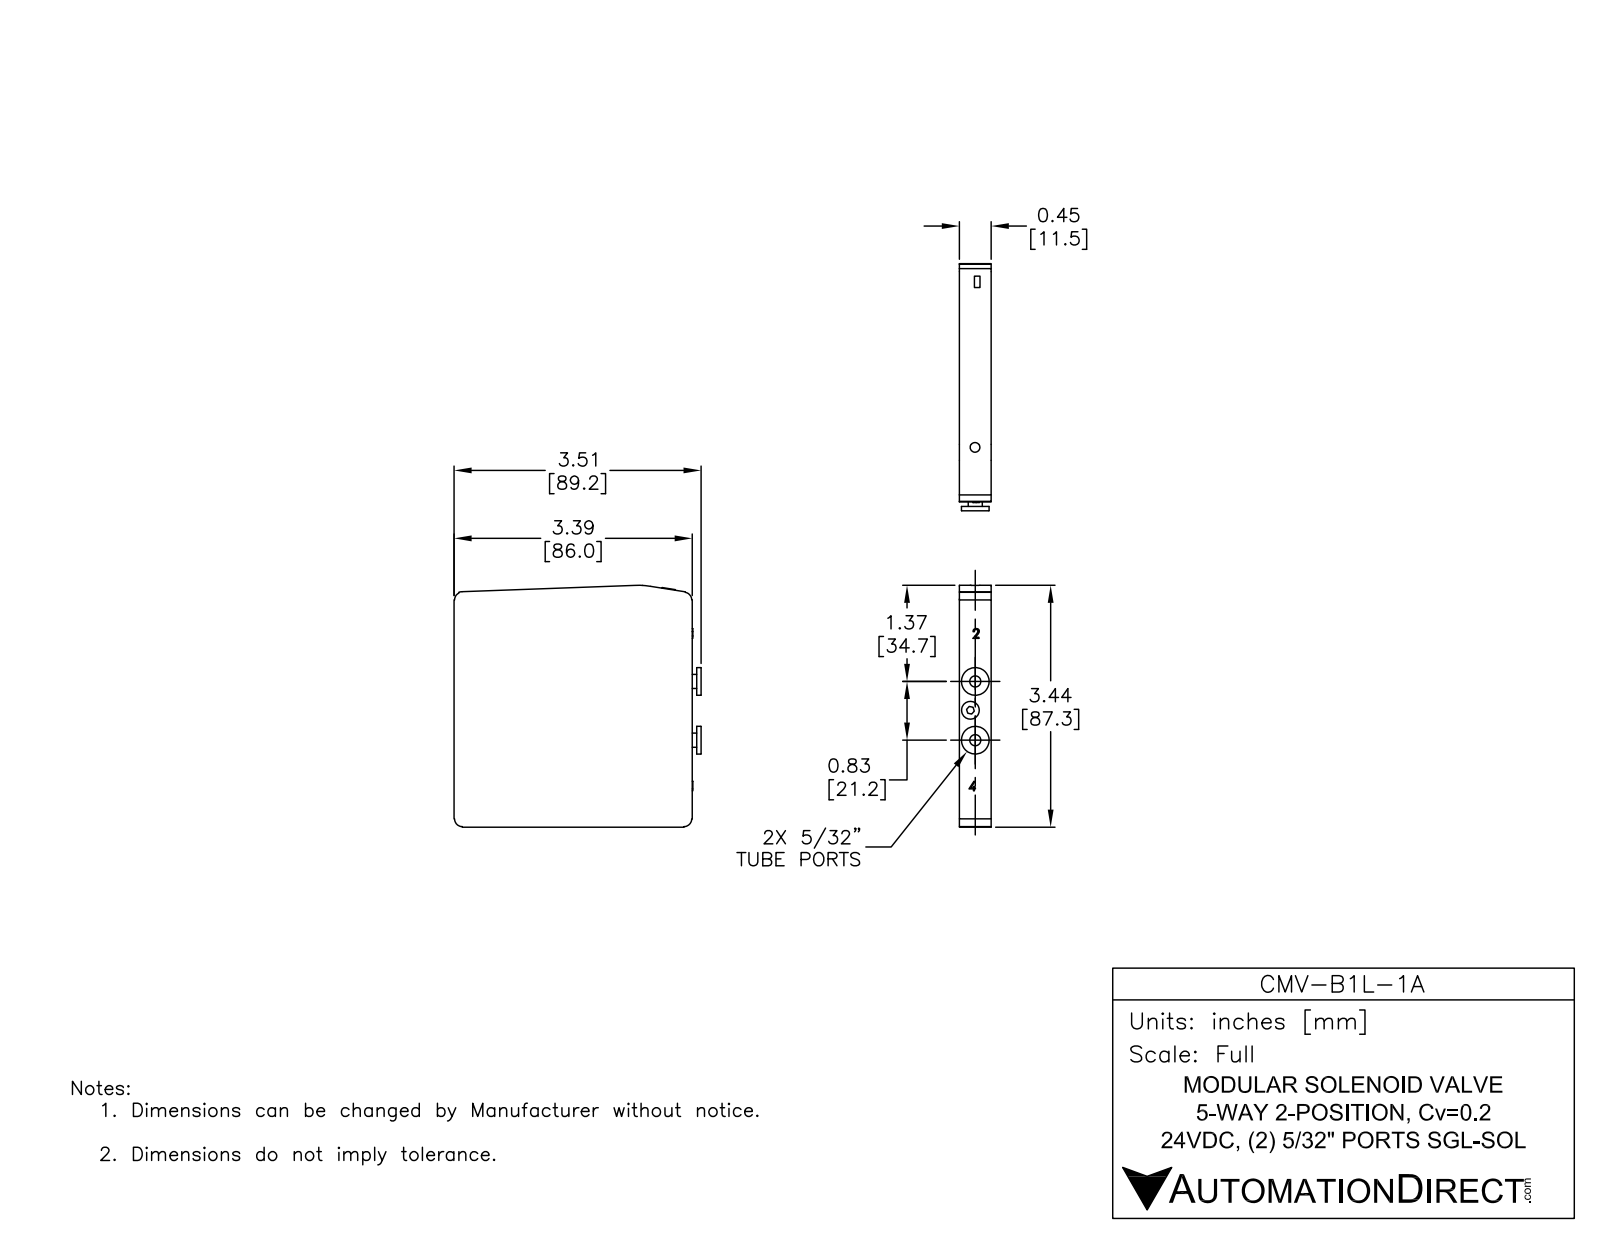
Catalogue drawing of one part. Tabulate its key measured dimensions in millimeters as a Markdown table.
| quantity | value |
| --- | --- |
| part name | CMV-B1L-1A |
| STEP written by | SolidWorks 2013 (AUTOMOTIVE_DESIGN) |
| units | millimeters |
| bodies | 78 solids, 1127 faces (871 planar, 159 cylindrical, 97 other) |
| overall size | 89.5 × 87.3 × 20.43 |
| volume | 78 599 mm³ |
| surface area | 44 618 mm² |
| round holes (diameter × count) | 5.25 × 4, 6.5 × 4, 4.4 × 2, 8 × 2, 9.5 × 2, 3.35 × 1, 3.6 × 1, 6.25 × 1 |
| round bosses / shafts (diameter × count) | 1.5 × 4, 10.8 × 2, 7.75 × 2, 6.25 × 2, 5.75 × 2, 4.2 × 2, 4 × 2, 3.5 × 1 |
| partial cylindrical surfaces (radius × count) | 2.35 × 12, 0.78 × 4, 1 × 4, 1.5 × 4, 2.8 × 4, 0.15 × 2, 0.25 × 2, 0.17 × 1 |
| main face-to-face distances | 11.5, 1.5, 10, 1, 3, 83, 2.5, 12.5, 10.83, 11.83 |
| hole center spacings | 9.7, 22.17, 8.66, 9.46, 10.28, 10.63, 11.02, 11.28 |
